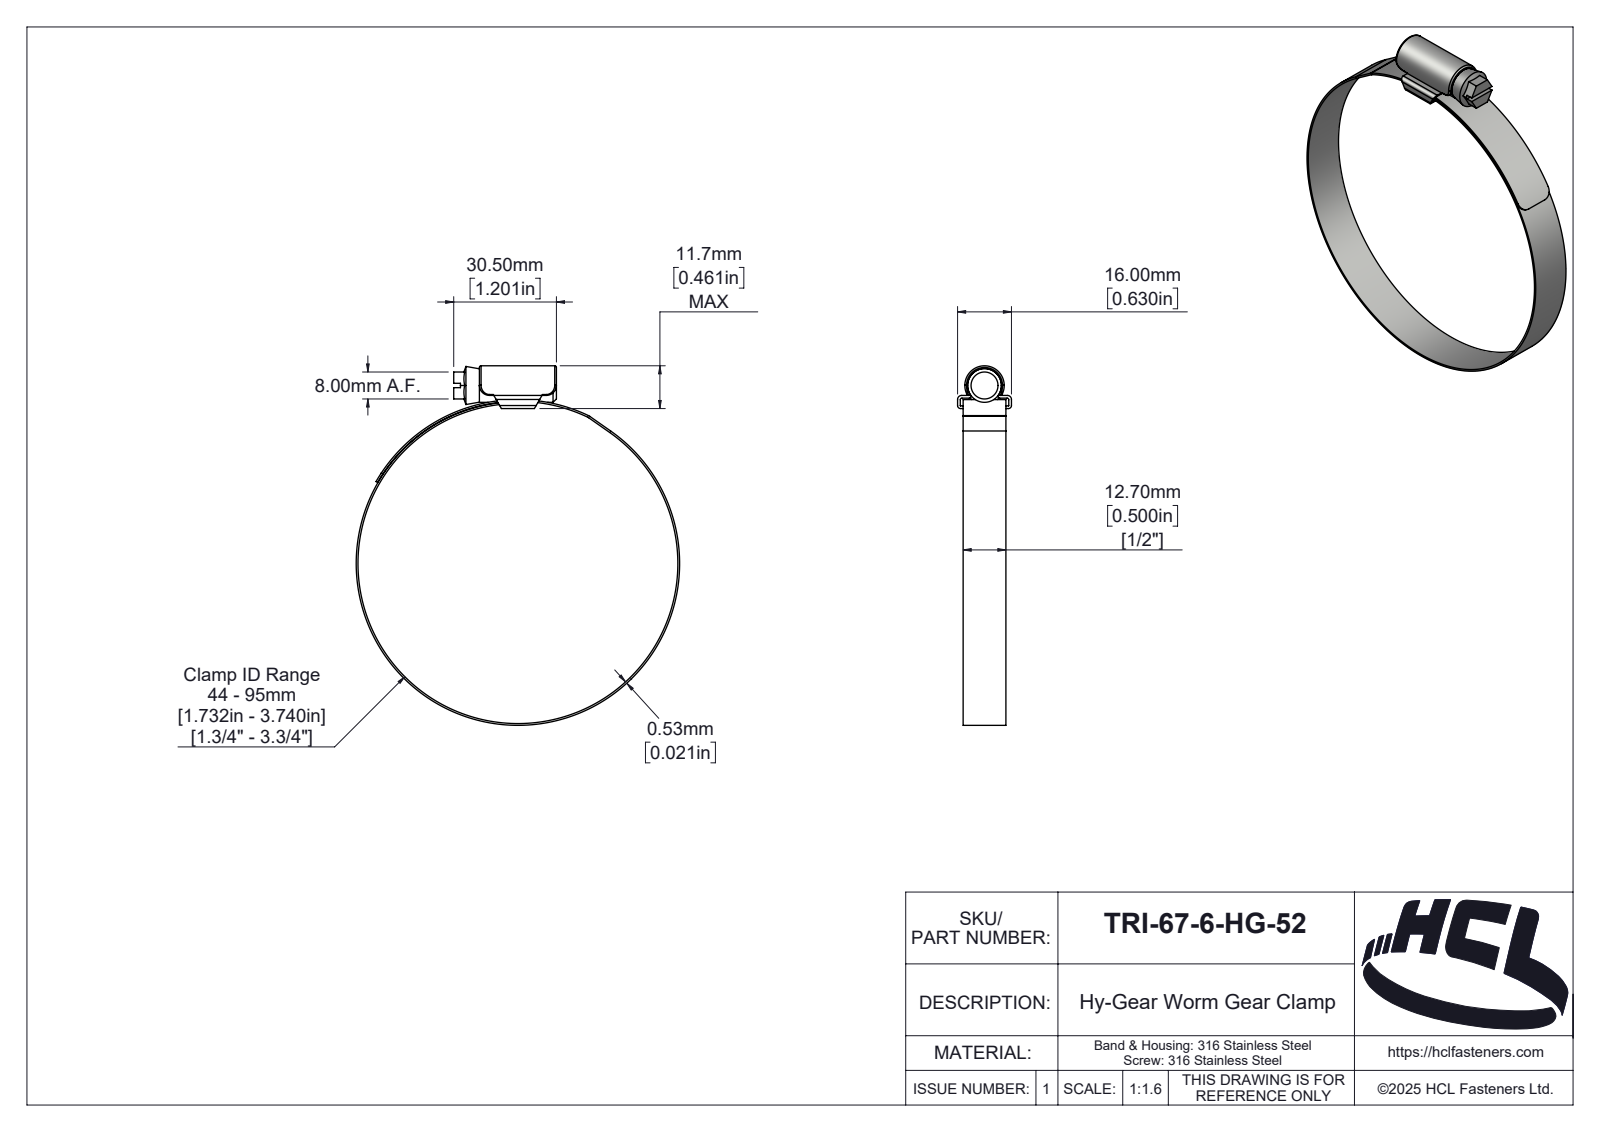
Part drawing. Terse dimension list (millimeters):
name: TRI-57-0-HG-52
written by: SolidWorks 2025 (AUTOMOTIVE_DESIGN)
unit: mm
bodies: 3 solids, 189 faces (39 planar, 89 cylindrical, 61 other)
size: 106.73 × 96.06 × 16
volume: 5 354 mm³; area: 12 195 mm²
holes: 1× ⌀95
bosses: 1× ⌀96.06, 1× ⌀10
rounds: 6× R0.5, 4× R3, 2× R0.1, 2× R0.9, 2× R1.2, 1× R0.46, 1× R1.89, 1× R2
face distances: 0.8, 12.7, 3.1, 0.53, 2.3, 3.9, 30.5, 1.65, 14.35, 15.2
